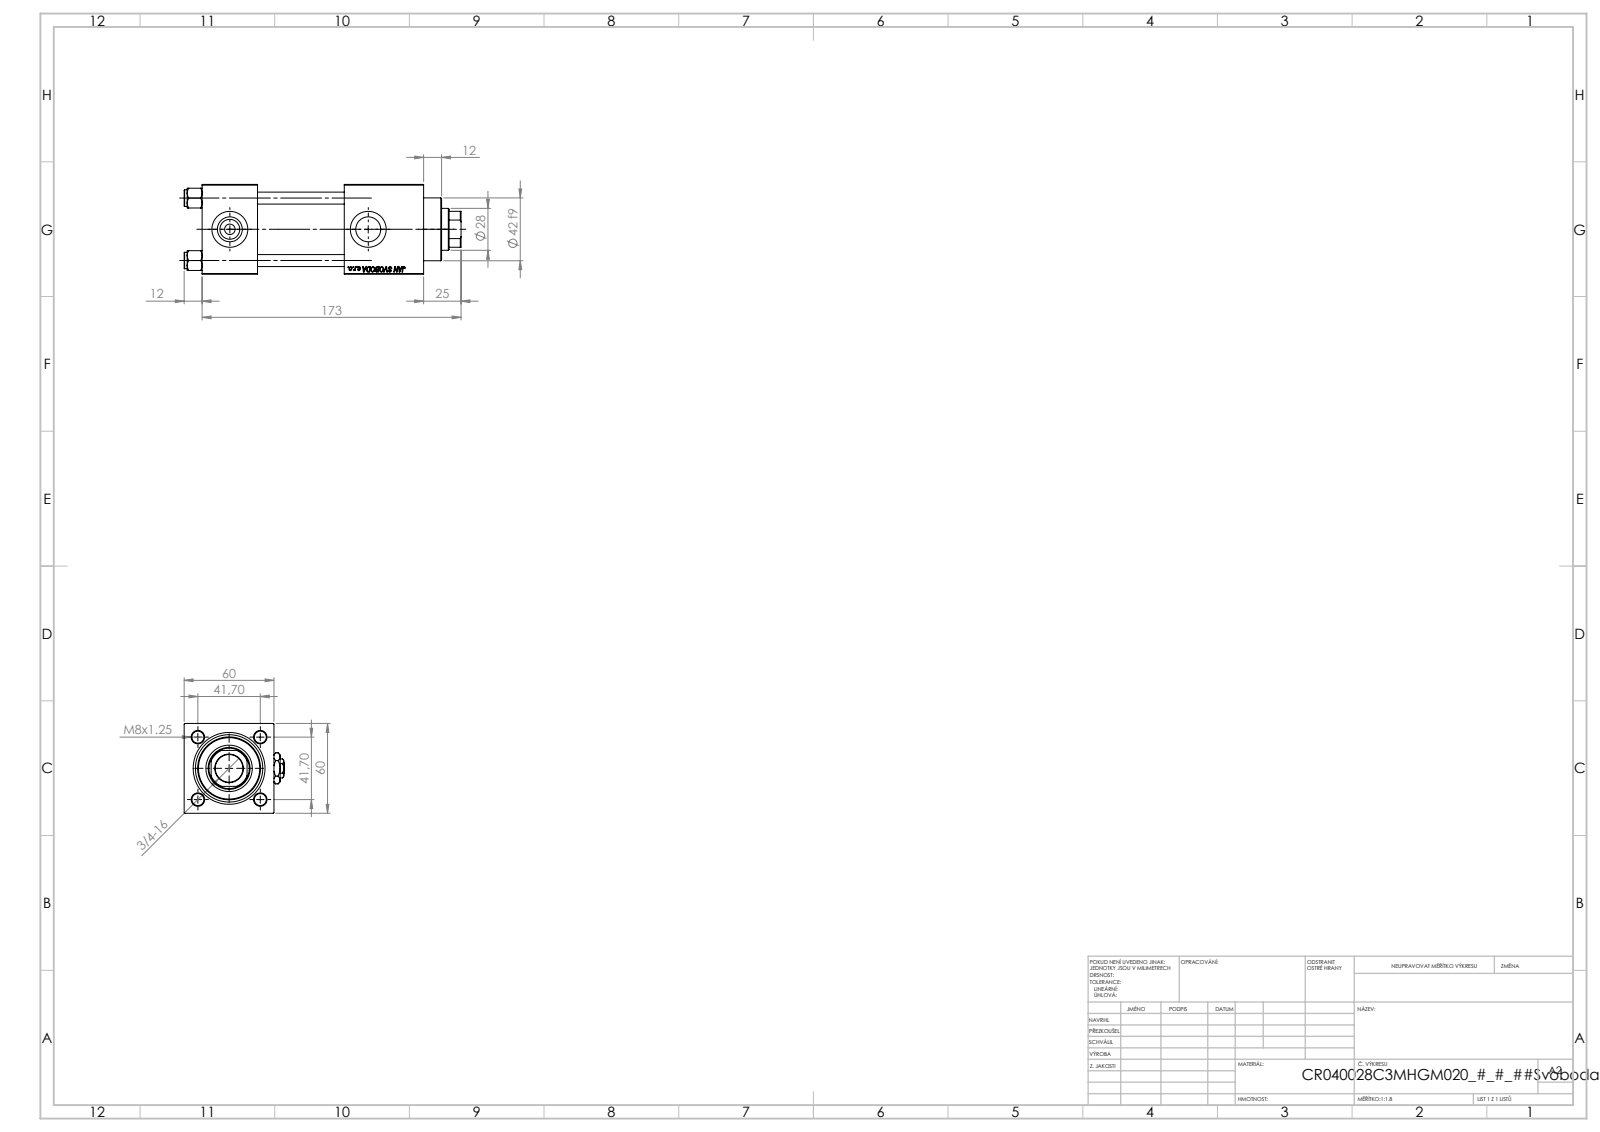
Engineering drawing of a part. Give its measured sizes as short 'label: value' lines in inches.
name: V215CR_C_TYCINKA; V215CR_VCP_C; V215_VC_A; Zatka_pro_OIL_PORT (+2 more)
written by: SolidWorks 2019 (CONFIG_CONTROL_DESIGN)
unit: in
bodies: 13 solids, 1250 faces (574 planar, 98 cylindrical, 578 other)
size: 7.283 × 2.638 × 2.362
volume: 25.69 in³; area: 177.2 in²
holes: 4× ⌀0.315, 2× ⌀0.276, 2× ⌀0.656, 2× ⌀0.945, 1× ⌀0.728, 1× ⌀1.102, 1× ⌀1.22, 1× ⌀1.575, 1× ⌀1.772
bosses: 4× ⌀0.433, 1× ⌀1.811, 1× ⌀1.654
rounds: 1× R0.531
face distances: 2.362, 1.457, 2.283, 3.74, 2.087, 4.697, 3.24, 0.957, 5.827, 4.37
hole spacings: 1.161, 1.642, 2.322, 3.642
